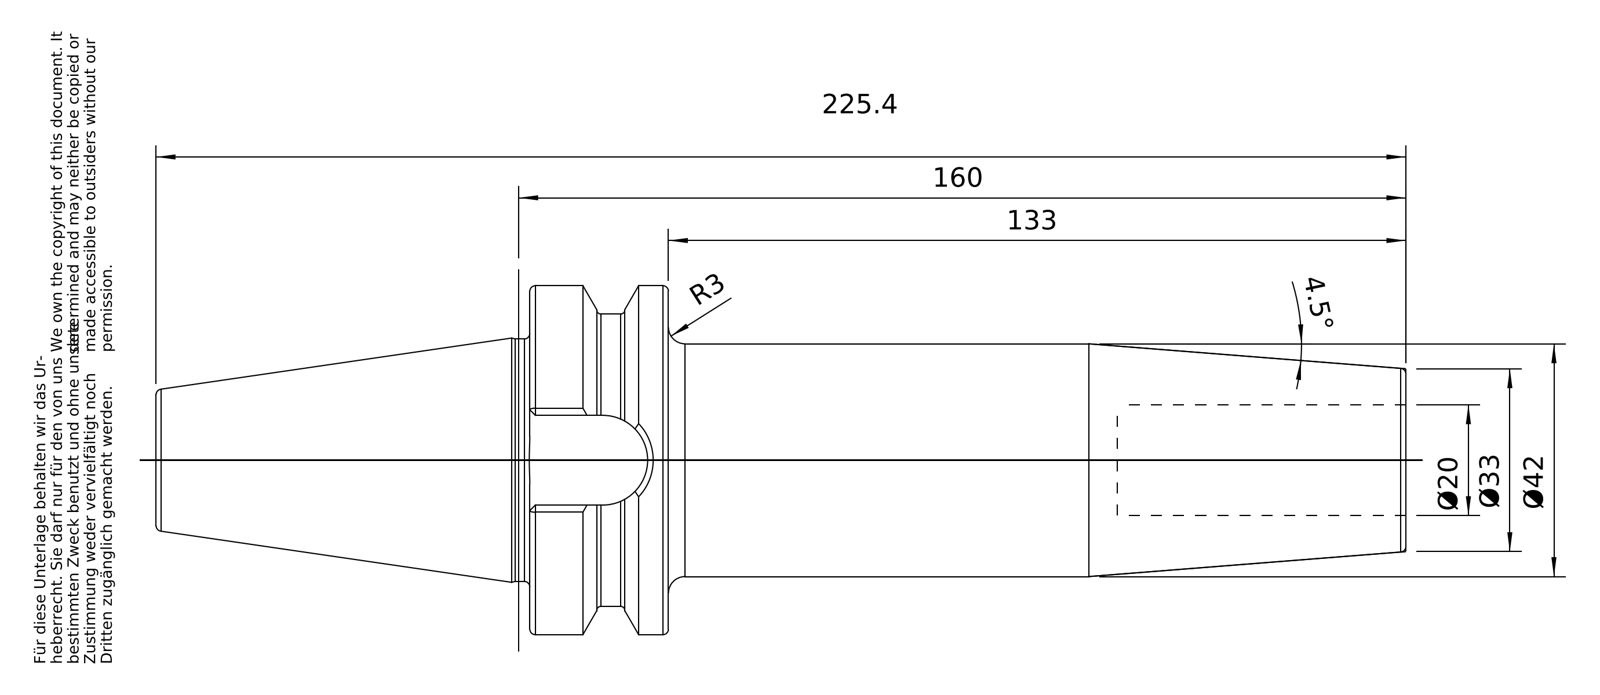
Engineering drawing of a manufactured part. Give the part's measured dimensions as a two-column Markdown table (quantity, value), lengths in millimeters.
| quantity | value |
| --- | --- |
| part name | 40-642-20 |
| STEP written by | PRO/ENGINEER BY PARAMETRIC TECHNOLOGY CORPORATION, 2010430 (CONFIG_CONTROL_DESIGN) |
| units | millimeters |
| bodies | 1 solid, 96 faces (26 planar, 22 cylindrical, 48 other) |
| overall size | 225.4 × 62.98 × 62.98 |
| volume | 278 552 mm³ |
| surface area | 41 129 mm² |
| round holes (diameter × count) | 13.84 × 1, 17.01 × 1, 17.5 × 1, 20 × 1 |
| round bosses / shafts (diameter × count) | 62.98 × 1, 52.75 × 1, 43.75 × 1, 42 × 1, 16.01 × 1 |
| partial cylindrical surfaces (radius × count) | 8.1 × 1 |
| main face-to-face distances | 25, 158, 133, 44.9, 106, 81, 52, 16.2, 67.4, 92.4 |
